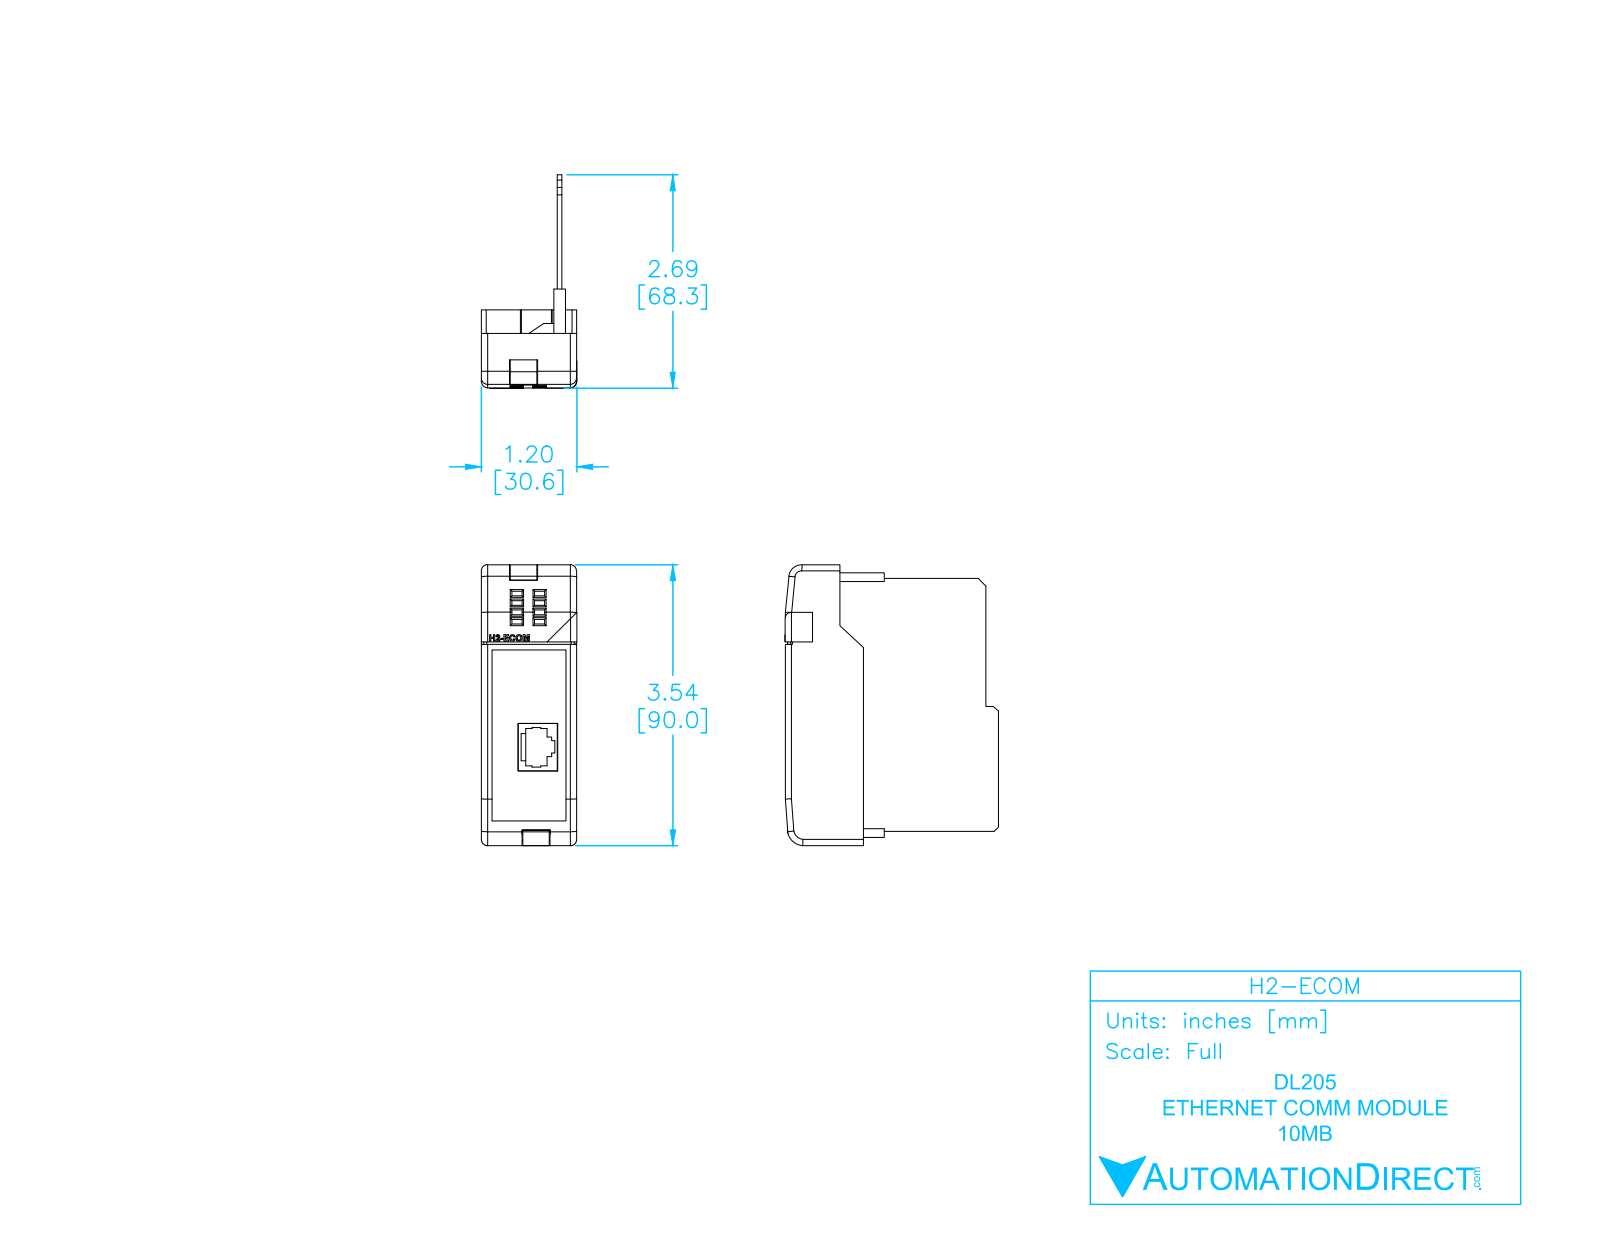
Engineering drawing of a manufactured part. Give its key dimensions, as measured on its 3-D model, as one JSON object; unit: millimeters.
{"part_name": "H2-ECOM", "step_written_by": "SolidWorks 2009 (AUTOMOTIVE_DESIGN)", "units": "millimeters", "bodies": {"solids": 2, "faces": 380, "planar": 257, "cylindrical": 85, "other": 38}, "overall_size": [90, 68.38, 30.55], "volume_mm3": 18927, "surface_area_mm2": 28848, "partial_cylinders_radius": [[0.5, 29], [2, 11], [0.25, 4], [1, 2], [2.62, 1], [3.79, 1], [4.12, 1], [5.29, 1]], "face_to_face_distances": [1.5, 4.72, 3.22, 6.22, 0.5, 24.28, 29, 25.78, 30.5, 27.5]}
